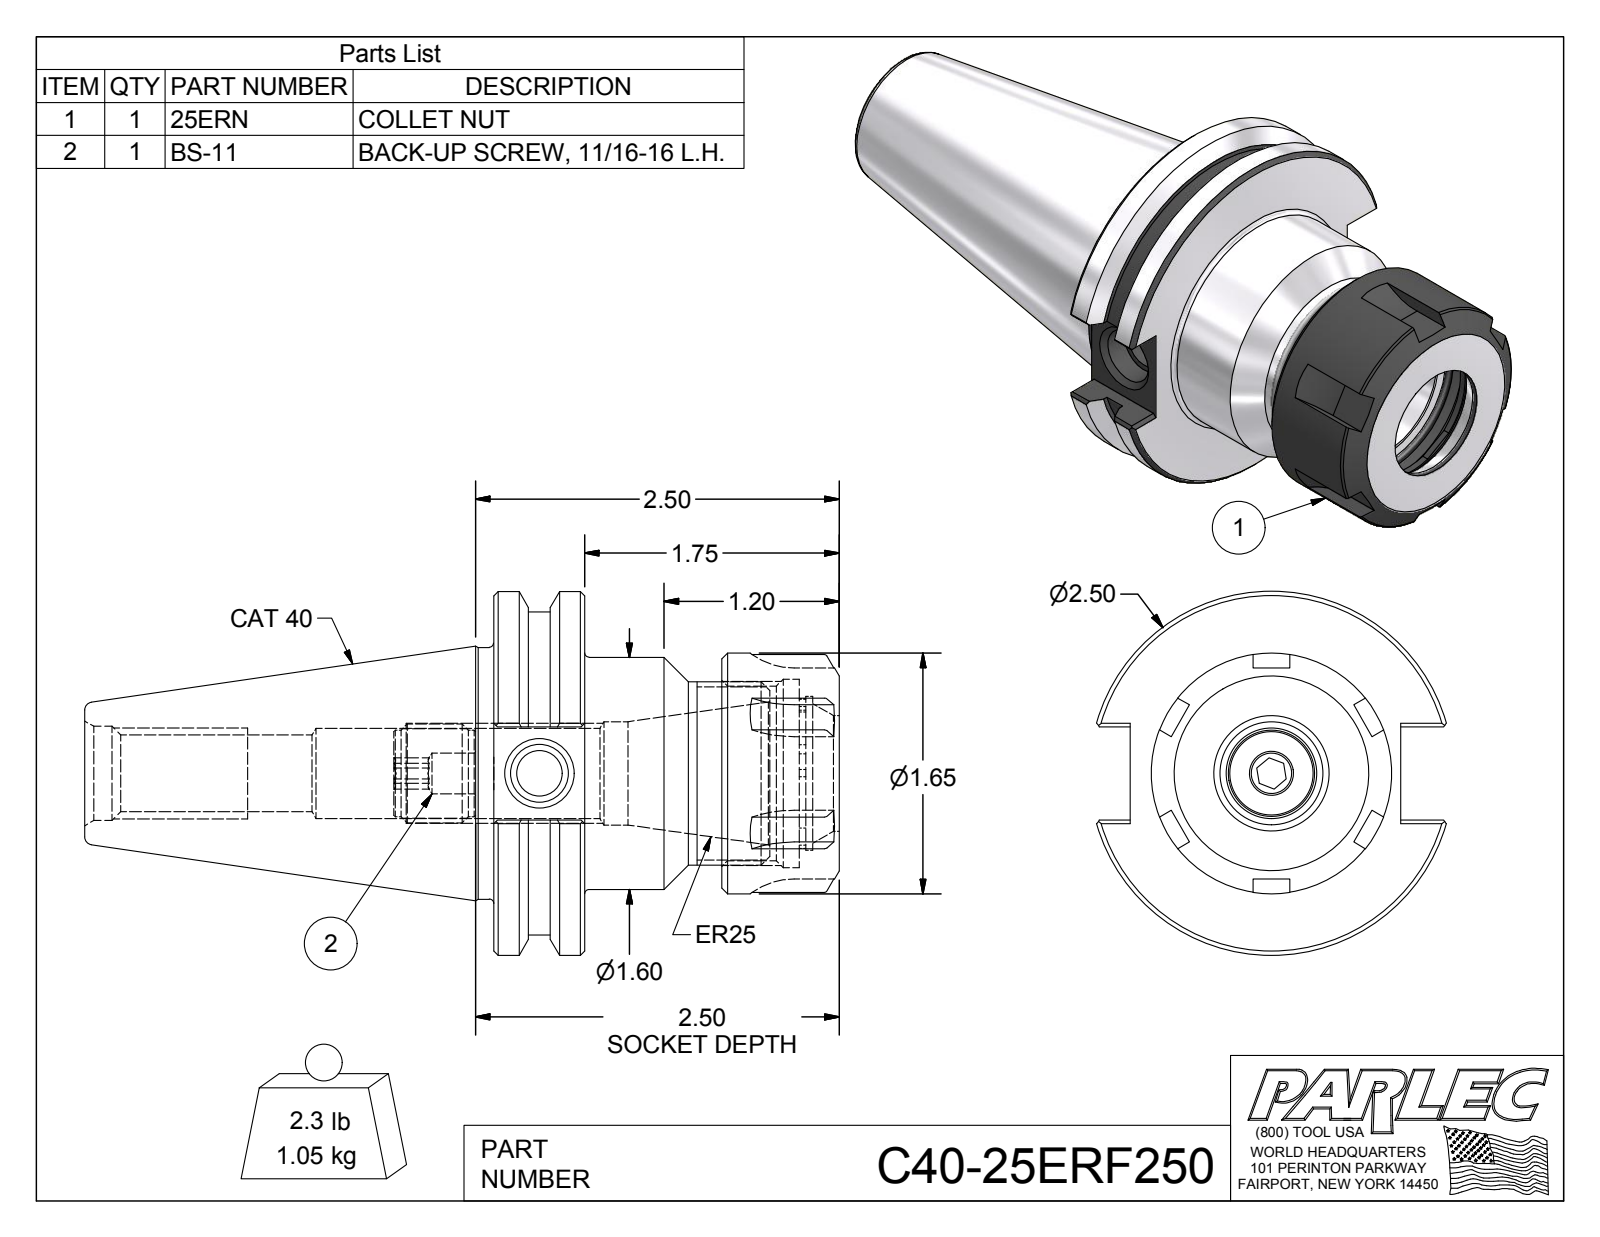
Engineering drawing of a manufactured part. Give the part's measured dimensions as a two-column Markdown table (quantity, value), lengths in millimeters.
| quantity | value |
| --- | --- |
| part name | C40-25ER2-1; 25ERN; BS-11; C40-25ERF250 |
| STEP written by | Autodesk Inventor 2016 (AUTOMOTIVE_DESIGN) |
| units | millimeters |
| bodies | 3 solids, 171 faces (74 planar, 38 cylindrical, 59 other) |
| overall size | 131.76 × 63.5 × 61.05 |
| volume | 136 672 mm³ |
| surface area | 33 683 mm² |
| round holes (diameter × count) | 7.11 × 1, 8 × 1, 10.05 × 1, 13.39 × 1, 15.75 × 1, 16.46 × 1, 18.03 × 1, 20.32 × 1, 30.5 × 1, 32.88 × 1 |
| round bosses / shafts (diameter × count) | 63.5 × 1, 56.36 × 1, 43.94 × 1, 42 × 1, 40.51 × 1, 32 × 1, 17.3 × 1, 15.11 × 1 |
| partial cylindrical surfaces (radius × count) | 0.51 × 12, 12 × 1, 13.06 × 1, 13.43 × 1 |
| main face-to-face distances | 15.88, 60.33, 44.45, 39.76, 23.88, 20.57, 53.23, 37.35, 13.47, 7.1 |
